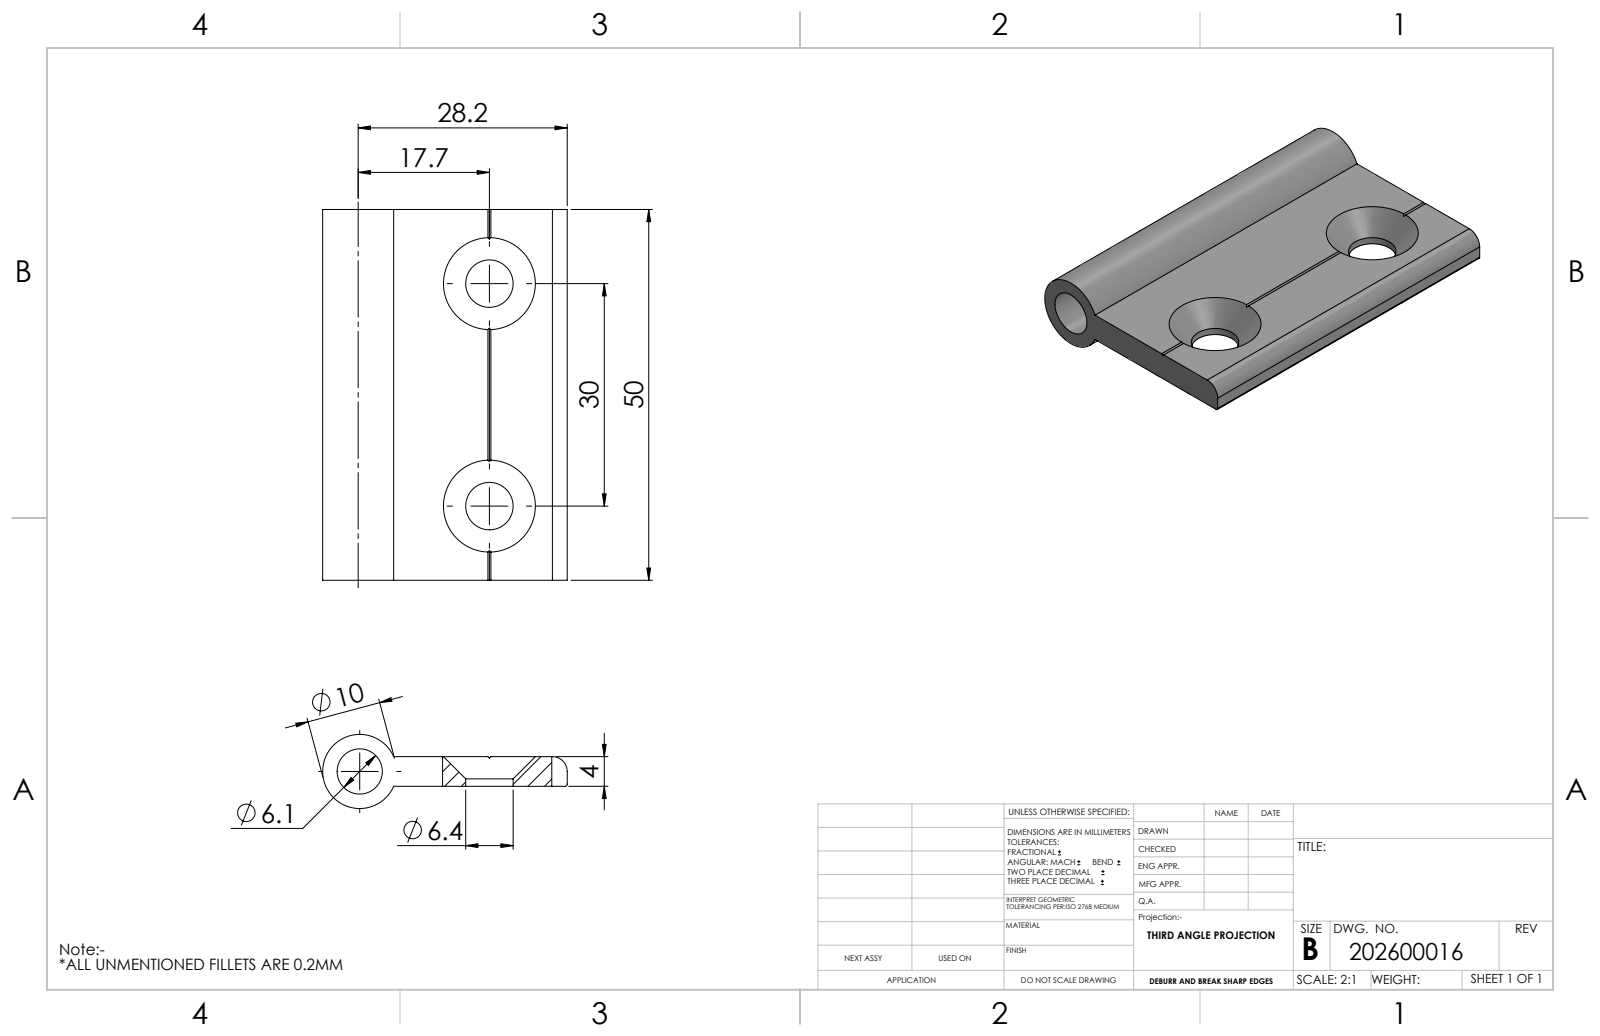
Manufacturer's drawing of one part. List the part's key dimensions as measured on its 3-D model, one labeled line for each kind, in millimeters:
Part name (STEP PRODUCT): 202600016
STEP written by: SolidWorks 2014 (AUTOMOTIVE_DESIGN)
Units: millimetres
Bodies: 1 solid, 26 faces (12 planar, 10 cylindrical, 4 other)
Overall size (bounding box): 50 × 33 × 10
Volume: 6 553 mm³ · Surface area: 5 087 mm²
Round holes (diameter × count): ⌀6.4 ×2, ⌀6.1 ×1
Round bosses / shafts (diameter × count): ⌀10 ×1
Partial cylindrical surfaces — rounded edges, fillets, slot ends (radius × count): R0.3 ×1, R2 ×1
Main face-to-face distances: 4, 50
Hole centre spacings: 30
